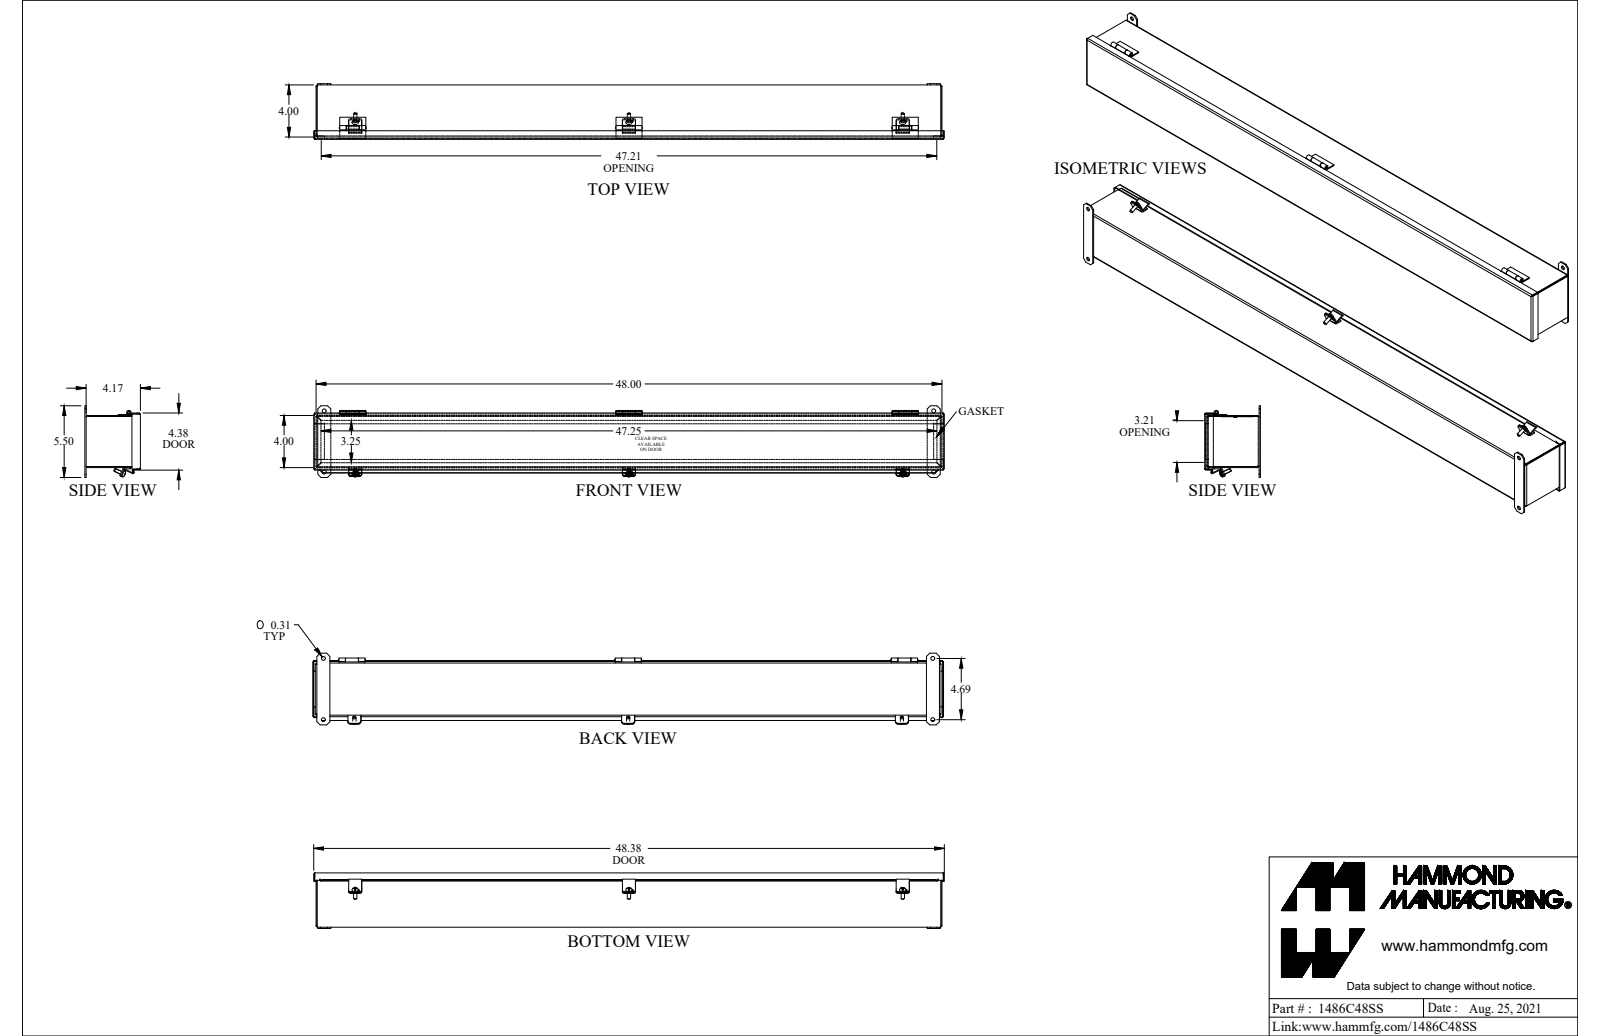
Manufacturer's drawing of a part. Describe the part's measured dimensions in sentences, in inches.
The part is named "1486C48SS". Its 3-D file was written by "SolidWorks 2021 (AUTOMOTIVE_DESIGN)". It is 9 solids with 536 faces: 346 planar, 145 cylindrical and 45 other. Overall it measures 48.375 by 5.5 by 4.267 inches. Its volume is 81.93 cubic inches and its surface area 2 050 square inches. Round holes: 4 of diameter 0.313, 3 of diameter 0.213, 1 of diameter 0.187. Round bosses or shafts: 3 of diameter 0.483, 3 of diameter 0.25, 1 of diameter 0.337, 1 of diameter 0.18. Partial cylindrical surfaces (rounded edges, fillets, slot ends): 13 of radius 0.036, 13 of radius 0.108, 12 of radius 0.188, 12 of radius 0.25, 6 of radius 0.01, 6 of radius 0.03, 6 of radius 0.141, 2 of radius 0.029. The main face-to-face distances are 0.072, 3.928, 4.1, 3.856, 4, 4.028, 4.172, 0.187, 0.259, 3.913. The hole center spacings are 4.688, 21, 46.75, 46.985, 42.
